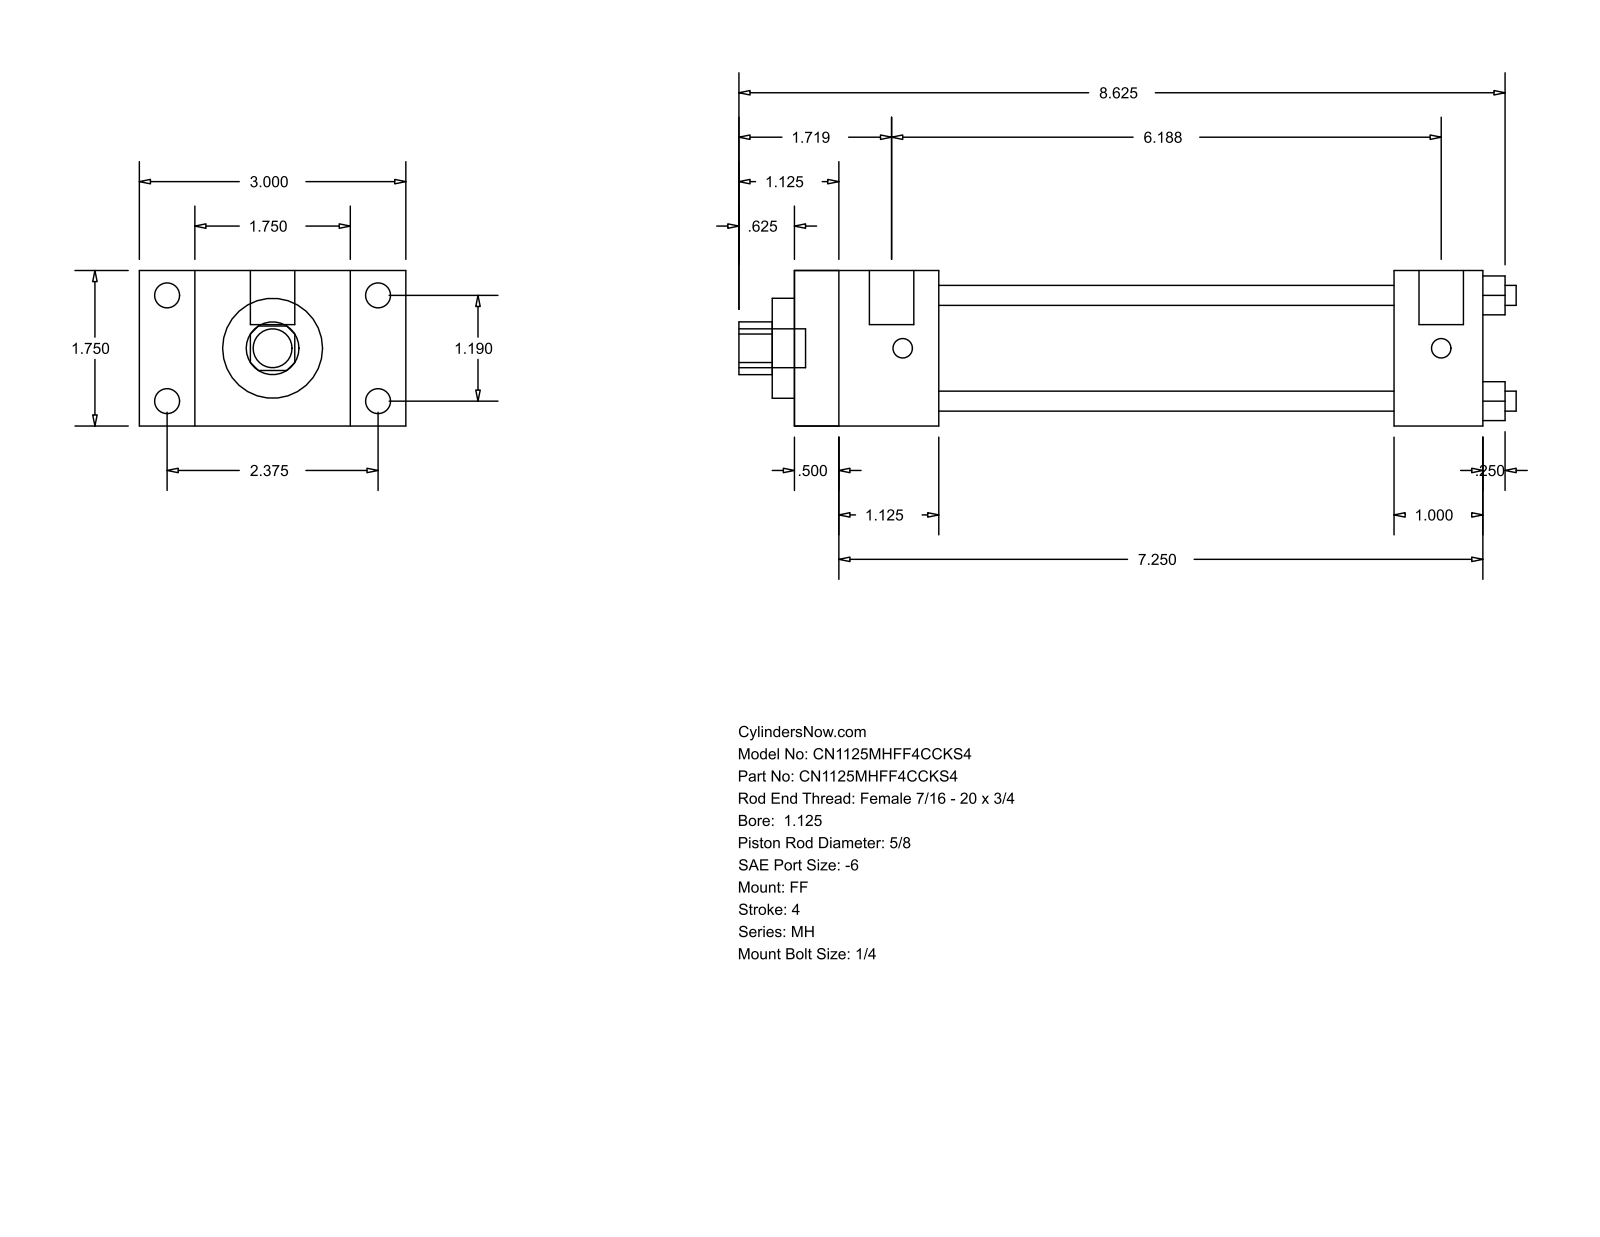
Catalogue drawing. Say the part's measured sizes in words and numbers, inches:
The part is named "MH_FF__0112_0.625". Its 3-D file was written by "GSSL Pune (CONFIG_CONTROL_DESIGN)". It is 0 solids with 92 faces: 64 planar, 28 cylindrical and 0 other. Overall it measures 8.75 by 3 by 1.75 inches. Round holes: 4 of diameter 0.225, 1 of diameter 0.625, 1 of diameter 1.125, 1 of diameter 1.375. Round bosses or shafts: 4 of diameter 0.281, 4 of diameter 0.219, 2 of diameter 0.5, 1 of diameter 0.437. Partial cylindrical surfaces (rounded edges, fillets, slot ends): 1 of radius 0.297. The main face-to-face distances are 1.75, 7.75, 0.5, 7.25, 0.625, 2.375, 1.125, 1.625, 6.75, 6.25. The hole center spacings are 0.841, 1.19, 1.683.
